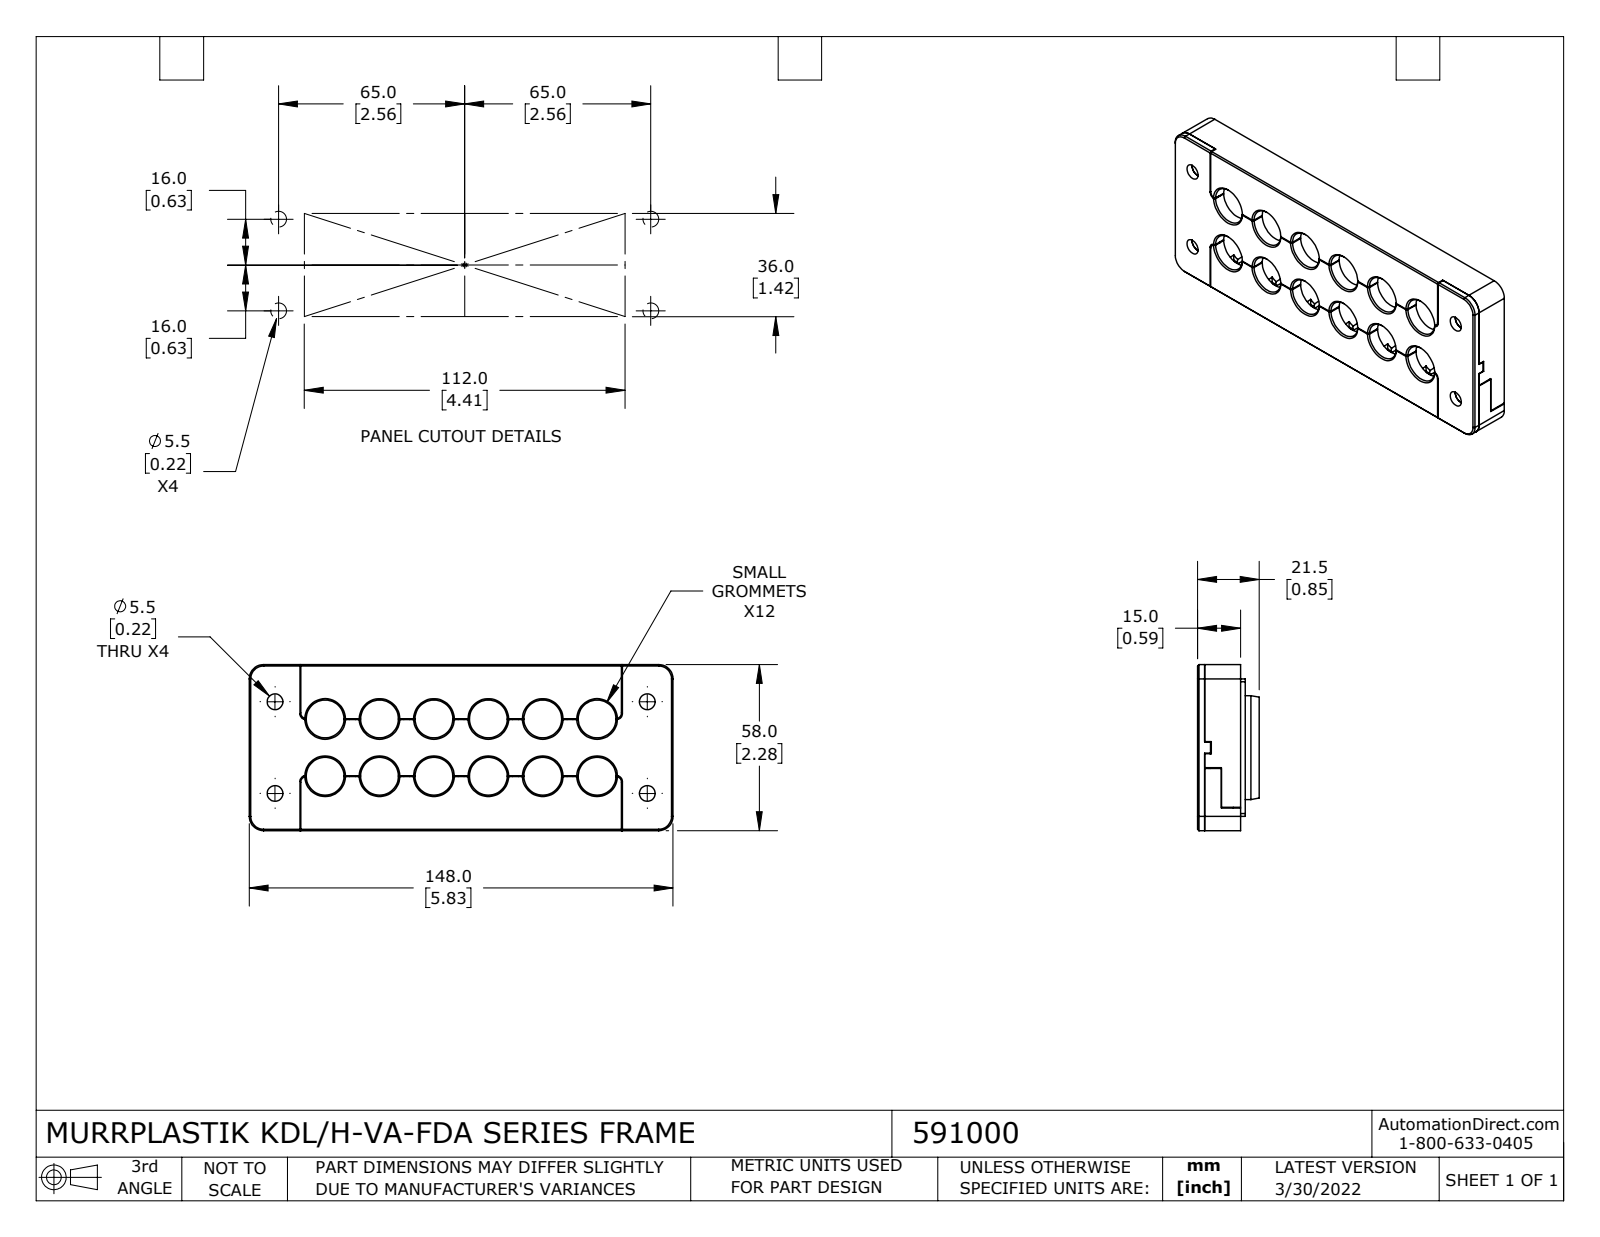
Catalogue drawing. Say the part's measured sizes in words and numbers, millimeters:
The part is named "591000". Its 3-D file was written by "SolidWorks 2021 (CONFIG_CONTROL_DESIGN)". It is 4 solids with 806 faces: 466 planar, 235 cylindrical and 105 other. Overall it measures 148 by 58 by 21.5 millimeters. Its volume is 100 000 cubic millimeters and its surface area 55 650 square millimeters. Round holes: 12 of diameter 13.2, 10 of diameter 15.1, 4 of diameter 5.5, 2 of diameter 6, 2 of diameter 15. Partial cylindrical surfaces (rounded edges, fillets, slot ends): 24 of radius 2, 10 of radius 1, 8 of radius 2.5, 6 of radius 0.5, 4 of radius 0.1, 4 of radius 0.2, 4 of radius 0.3, 4 of radius 0.4. The main face-to-face distances are 4.5, 2.5, 2, 5, 12.5, 14, 19, 53.5, 4, 10. The hole center spacings are 19, 27.6, 38, 43, 20, 57, 60.4, 76.
